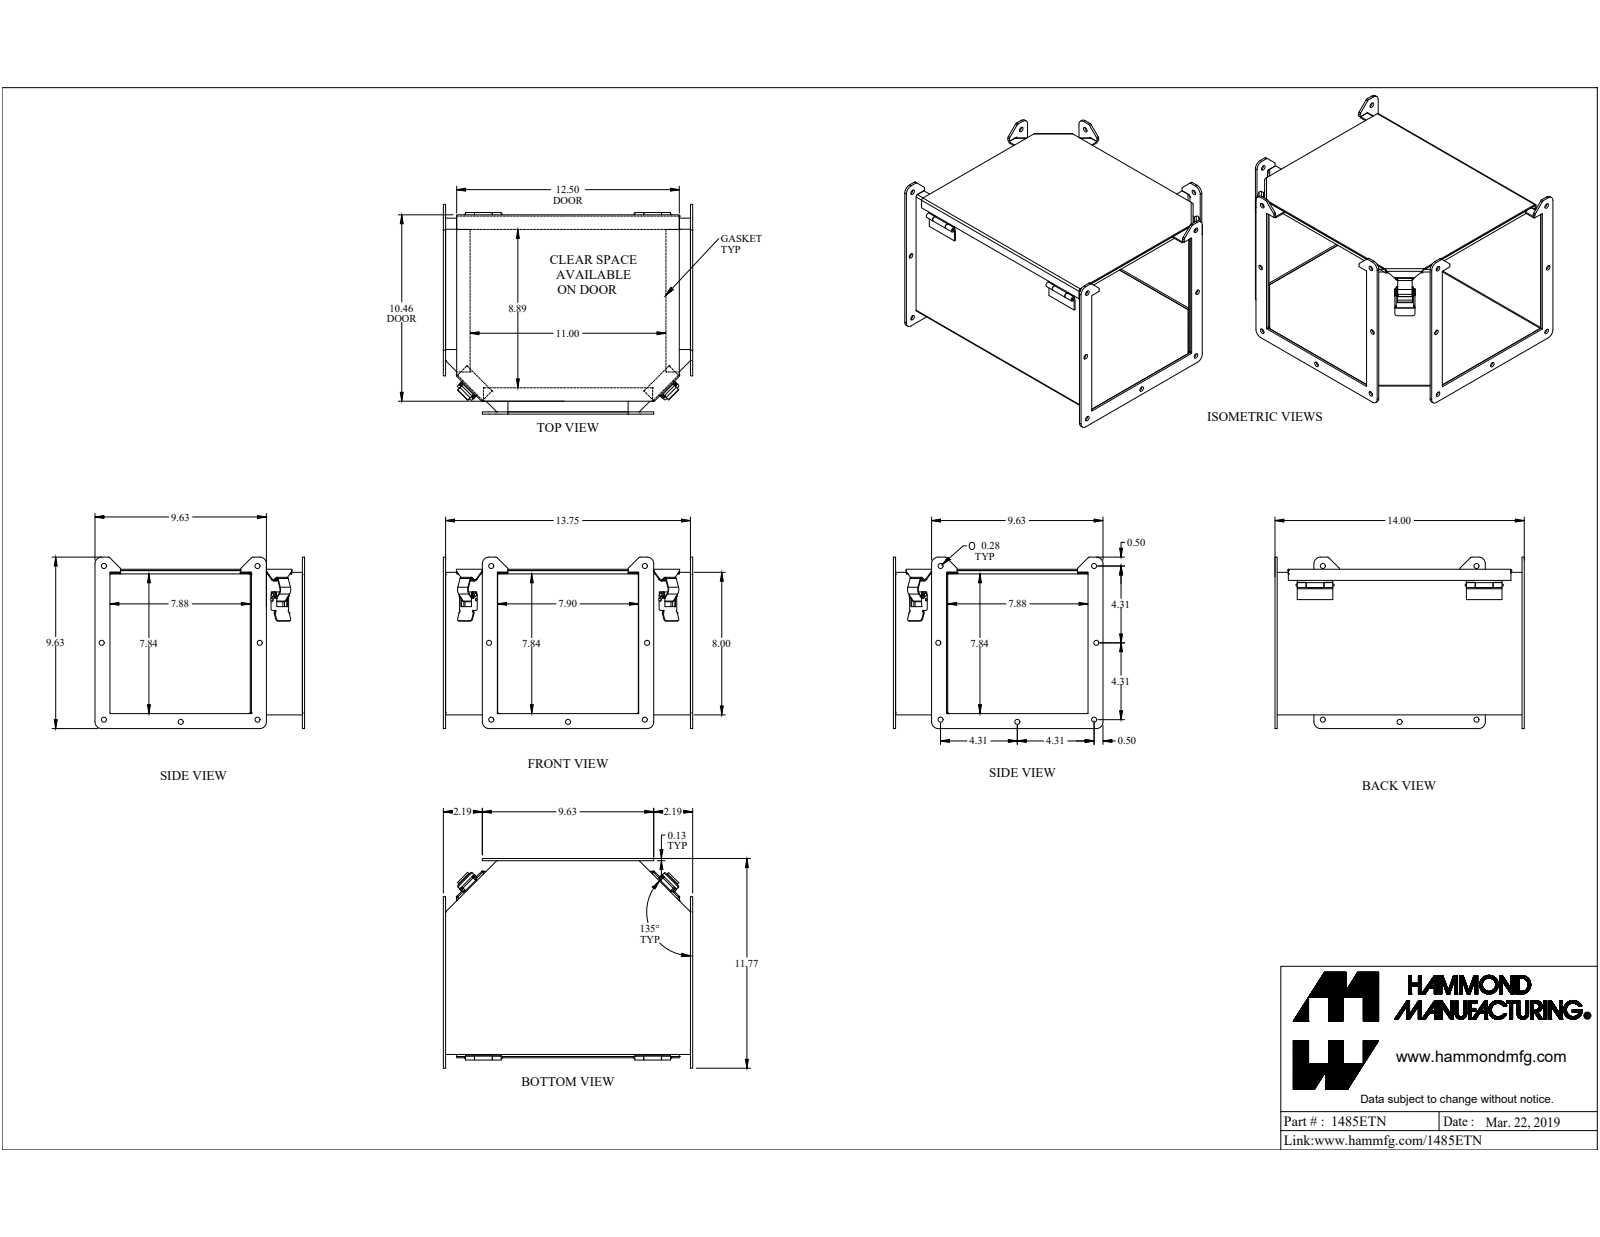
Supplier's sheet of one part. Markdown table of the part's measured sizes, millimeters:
| quantity | value |
| --- | --- |
| part name | 1485ETN |
| STEP written by | SolidWorks 2019 (CONFIG_CONTROL_DESIGN) |
| units | millimeters |
| bodies | 23 solids, 535 faces (322 planar, 185 cylindrical, 28 other) |
| overall size | 355.6 × 299 × 244.5 |
| volume | 809 000 mm³ |
| surface area | 792 900 mm² |
| round holes (diameter × count) | 7.1 × 14, 3.3 × 4, 4.2 × 4, 3.2 × 1 |
| round bosses / shafts (diameter × count) | 4.7 × 6, 4 × 4, 3.2 × 2, 7 × 1 |
| partial cylindrical surfaces (radius × count) | 0.4 × 14, 3.2 × 14, 0.9 × 11, 2.7 × 11, 1 × 8, 9.5 × 8, 0.9 × 6, 1.9 × 6 |
| main face-to-face distances | 1.8, 205.7, 203.9, 207.6, 3.2, 352.4, 4.4, 201.4, 6.6, 4.7 |
| hole center spacings | 7.2, 109.6, 247.8, 219.1, 109.6, 247.8, 159.4, 219.1 |
